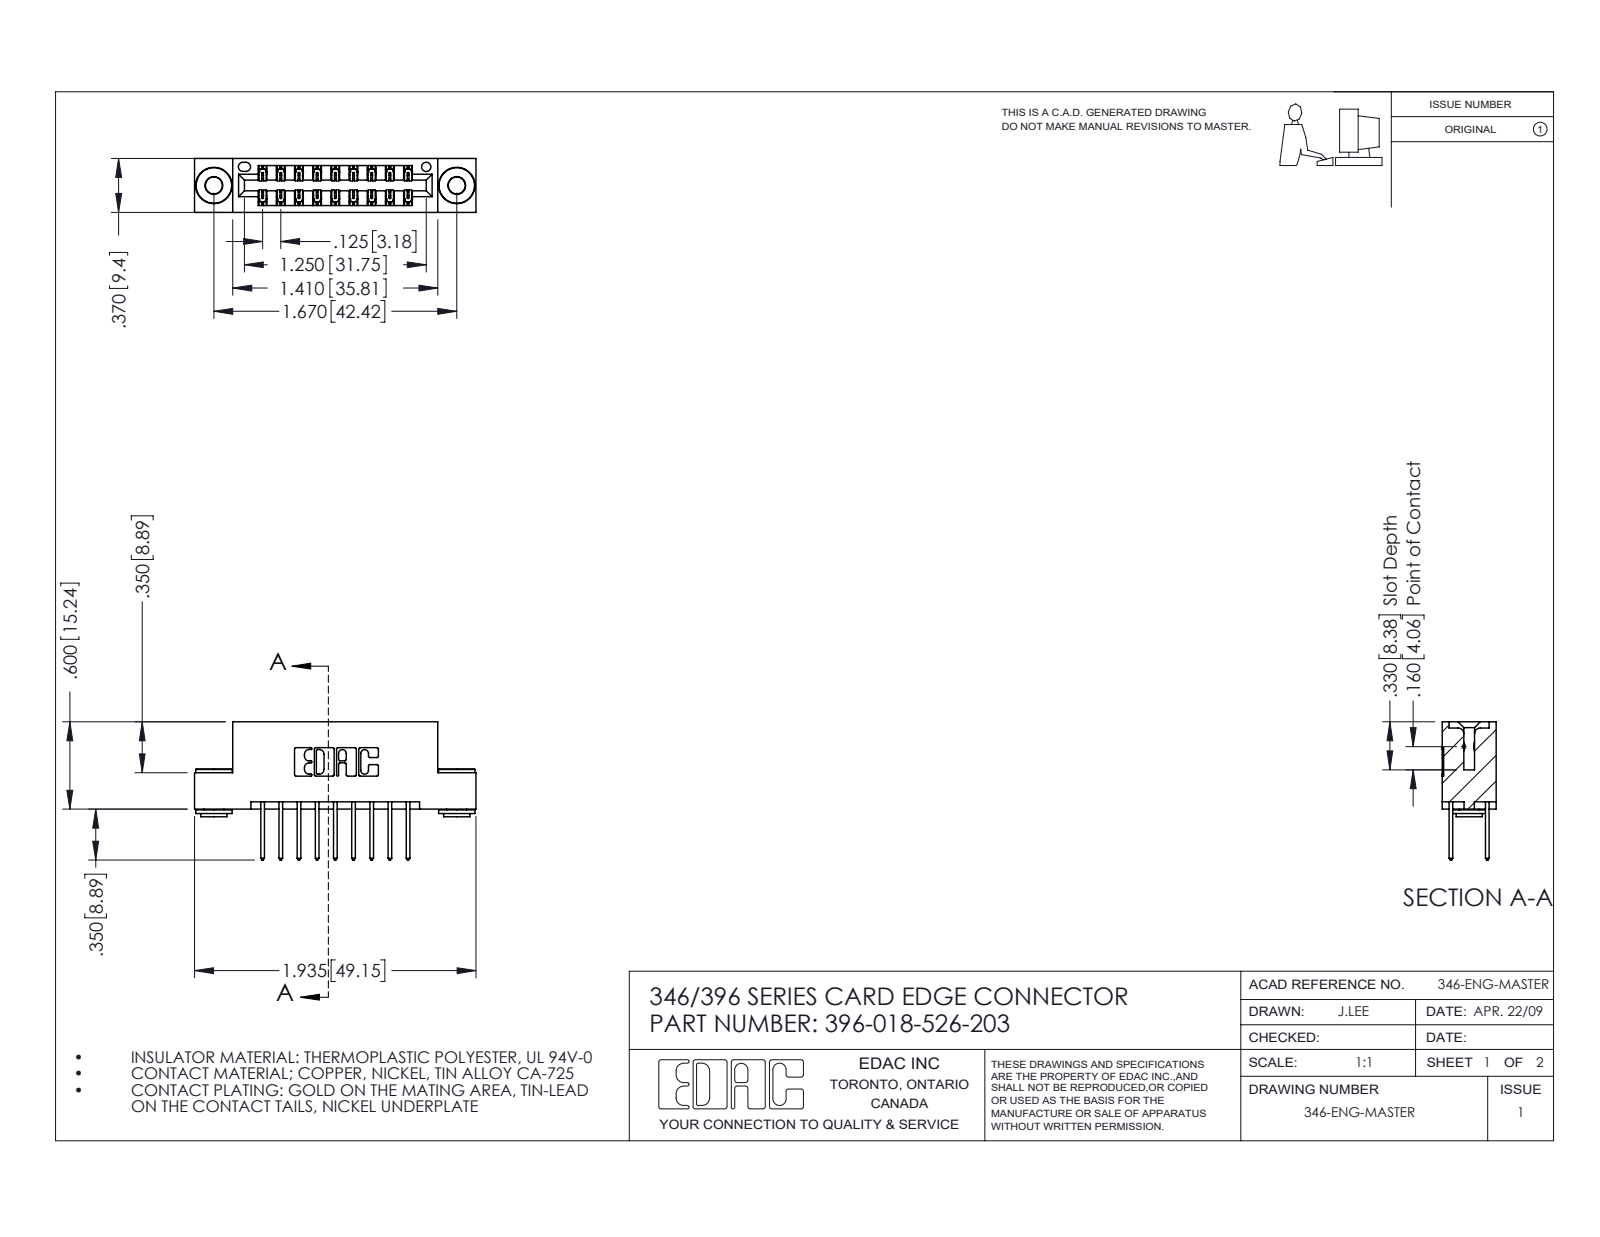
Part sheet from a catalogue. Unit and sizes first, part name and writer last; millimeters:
Units: millimetres
Overall size (bounding box): 49.1 × 24.1 × 9.4
Round holes (diameter × count): ⌀2.9 ×2, ⌀4 ×2, ⌀1.6 ×1
Round bosses / shafts (diameter × count): ⌀6.4 ×2, ⌀4.6 ×2, ⌀3.5 ×2
Partial cylindrical surfaces — rounded edges, fillets, slot ends (radius × count): R0.2 ×27, R0.3 ×22, R0.3 ×18, R0.2 ×6, R0.8 ×6, R0.7 ×3, R0.4 ×2, R0.6 ×2
Main face-to-face distances: 6.4, 1.2, 8.2, 9.4, 0.6, 1.8, 7.6, 7, 3.8, 5.6
Hole centre spacings: 6.2, 37.2, 42.4
Volume: 4 590 mm³ · Surface area: 6 130 mm²
Bodies: 21 solids, 1096 faces (716 planar, 372 cylindrical, 8 other)
Part name (STEP PRODUCT): 396-018-526-203; 345-292-001_345-293-126; 346 Part_Flush Mounting Lugs - 0.156 Dia-TH; 345-250-002_345-250-002-102
STEP written by: SolidWorks 2016 (CONFIG_CONTROL_DESIGN)
